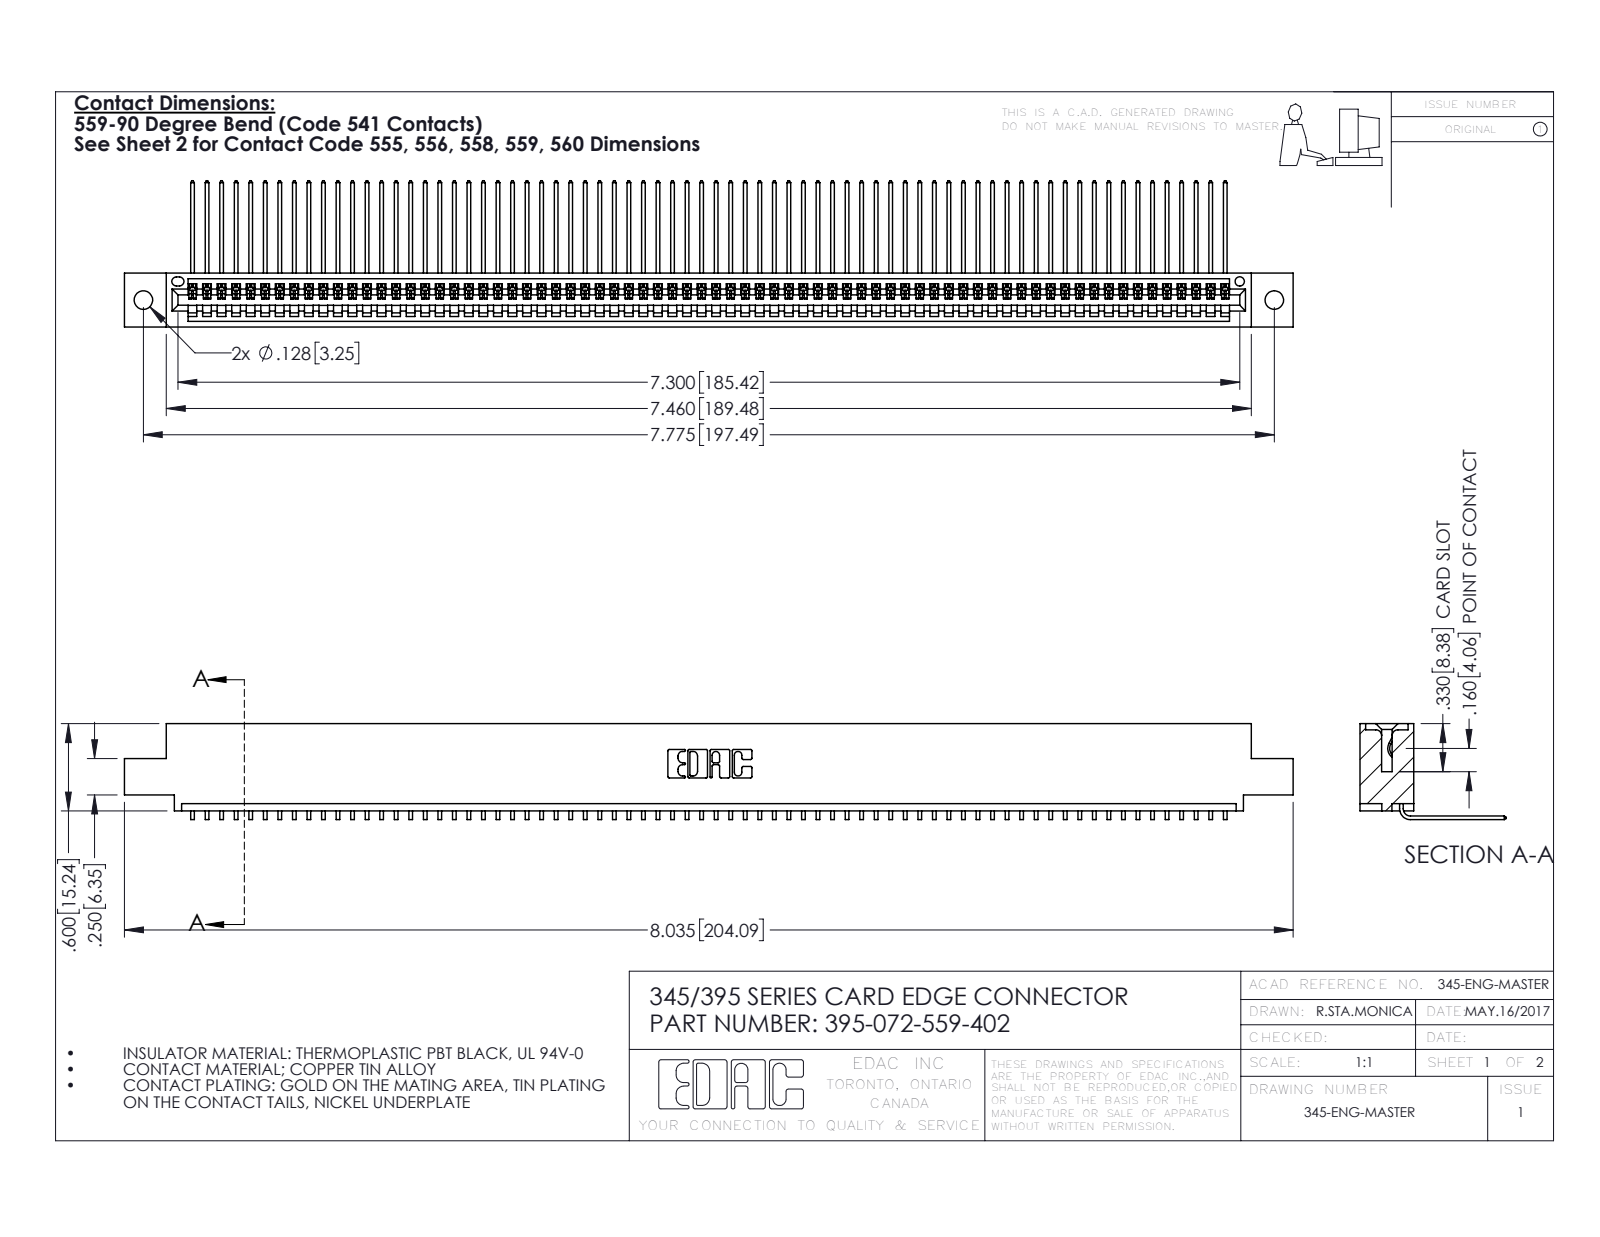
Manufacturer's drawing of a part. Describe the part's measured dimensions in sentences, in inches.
The part is named "395-072-559-402; 345 Part_0.110 Offset - 0.128 Dia; 345-292-001_558 559 Tail - 1". Its 3-D file was written by "SolidWorks 2016 (CONFIG_CONTROL_DESIGN)". It is 73 solids with 4450 faces: 3108 planar, 1342 cylindrical and 0 other. Overall it measures 8.035 by 1.005 by 0.659 inches. Its volume is 1.206 cubic inches and its surface area 43.23 square inches. Round holes: 2 of diameter 0.128, 1 of diameter 0.064. Partial cylindrical surfaces (rounded edges, fillets, slot ends): 144 of radius 0.006, 22 of radius 0.01, 6 of radius 0.007, 6 of radius 0.031, 3 of radius 0.026, 2 of radius 0.031, 2 of radius 0.04, 1 of radius 0.014. The main face-to-face distances are 0.072, 0.298, 0.37, 0.2, 0.098, 0.272, 0.025, 0.225, 0.149, 0.072. The hole center spacings are 0.27, 7.539, 7.775.
